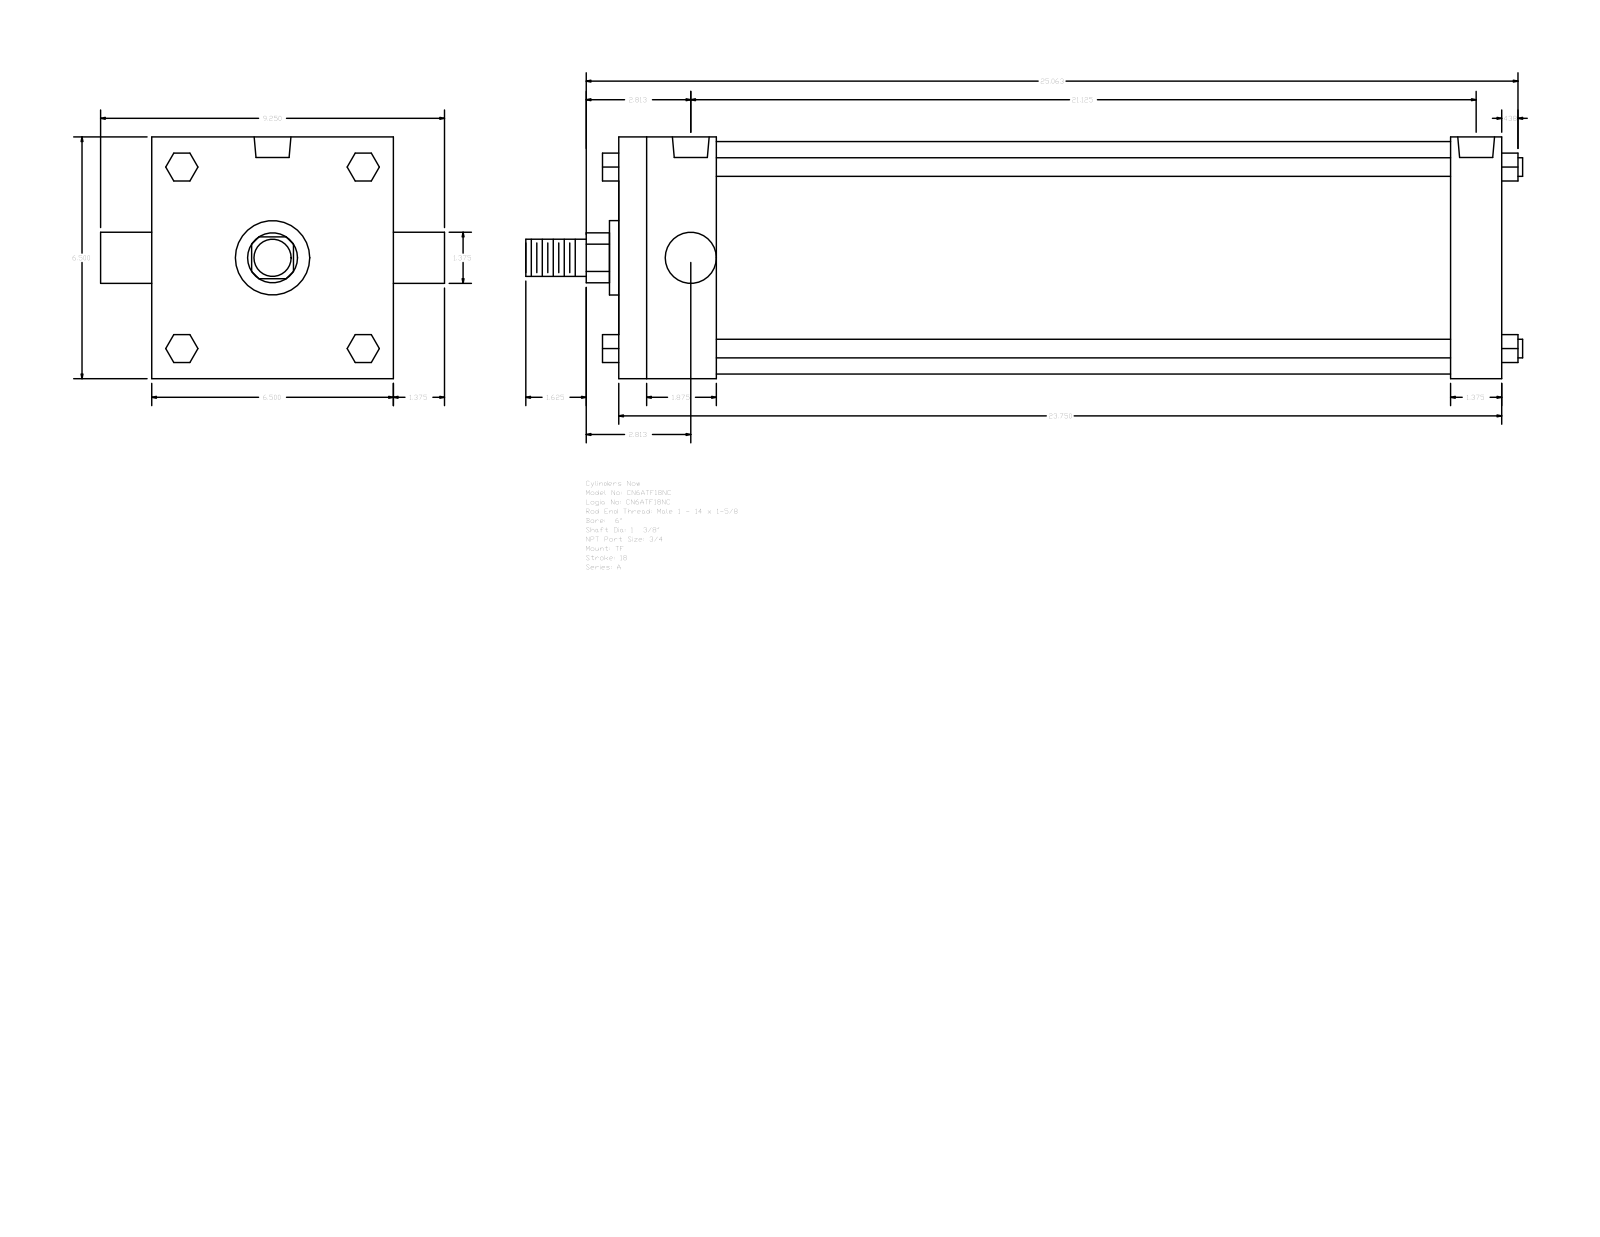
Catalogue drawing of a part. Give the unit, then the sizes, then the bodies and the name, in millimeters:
Units: millimetres
Overall size (bounding box): 681.04 × 234.95 × 165.1
Round holes (diameter × count): ⌀15.08 ×3, ⌀25.12 ×2
Round bosses / shafts (diameter × count): ⌀12.7 ×4, ⌀34.92 ×2, ⌀158.75 ×1, ⌀50.8 ×1, ⌀25.4 ×1
Partial cylindrical surfaces — rounded edges, fillets, slot ends (radius × count): R17.06 ×1
Main face-to-face distances: 165.1, 603.25, 66.67, 536.58, 568.32, 501.65, 34.93, 19.05, 61.97, 107.34
Hole centre spacings: 5.56, 531.01, 525.45, 536.57
Bodies: 0 solids, 120 faces (92 planar, 28 cylindrical, 0 other)
Part name (STEP PRODUCT): A_TF__0600_1.375
STEP written by: GSSL Pune (CONFIG_CONTROL_DESIGN)
